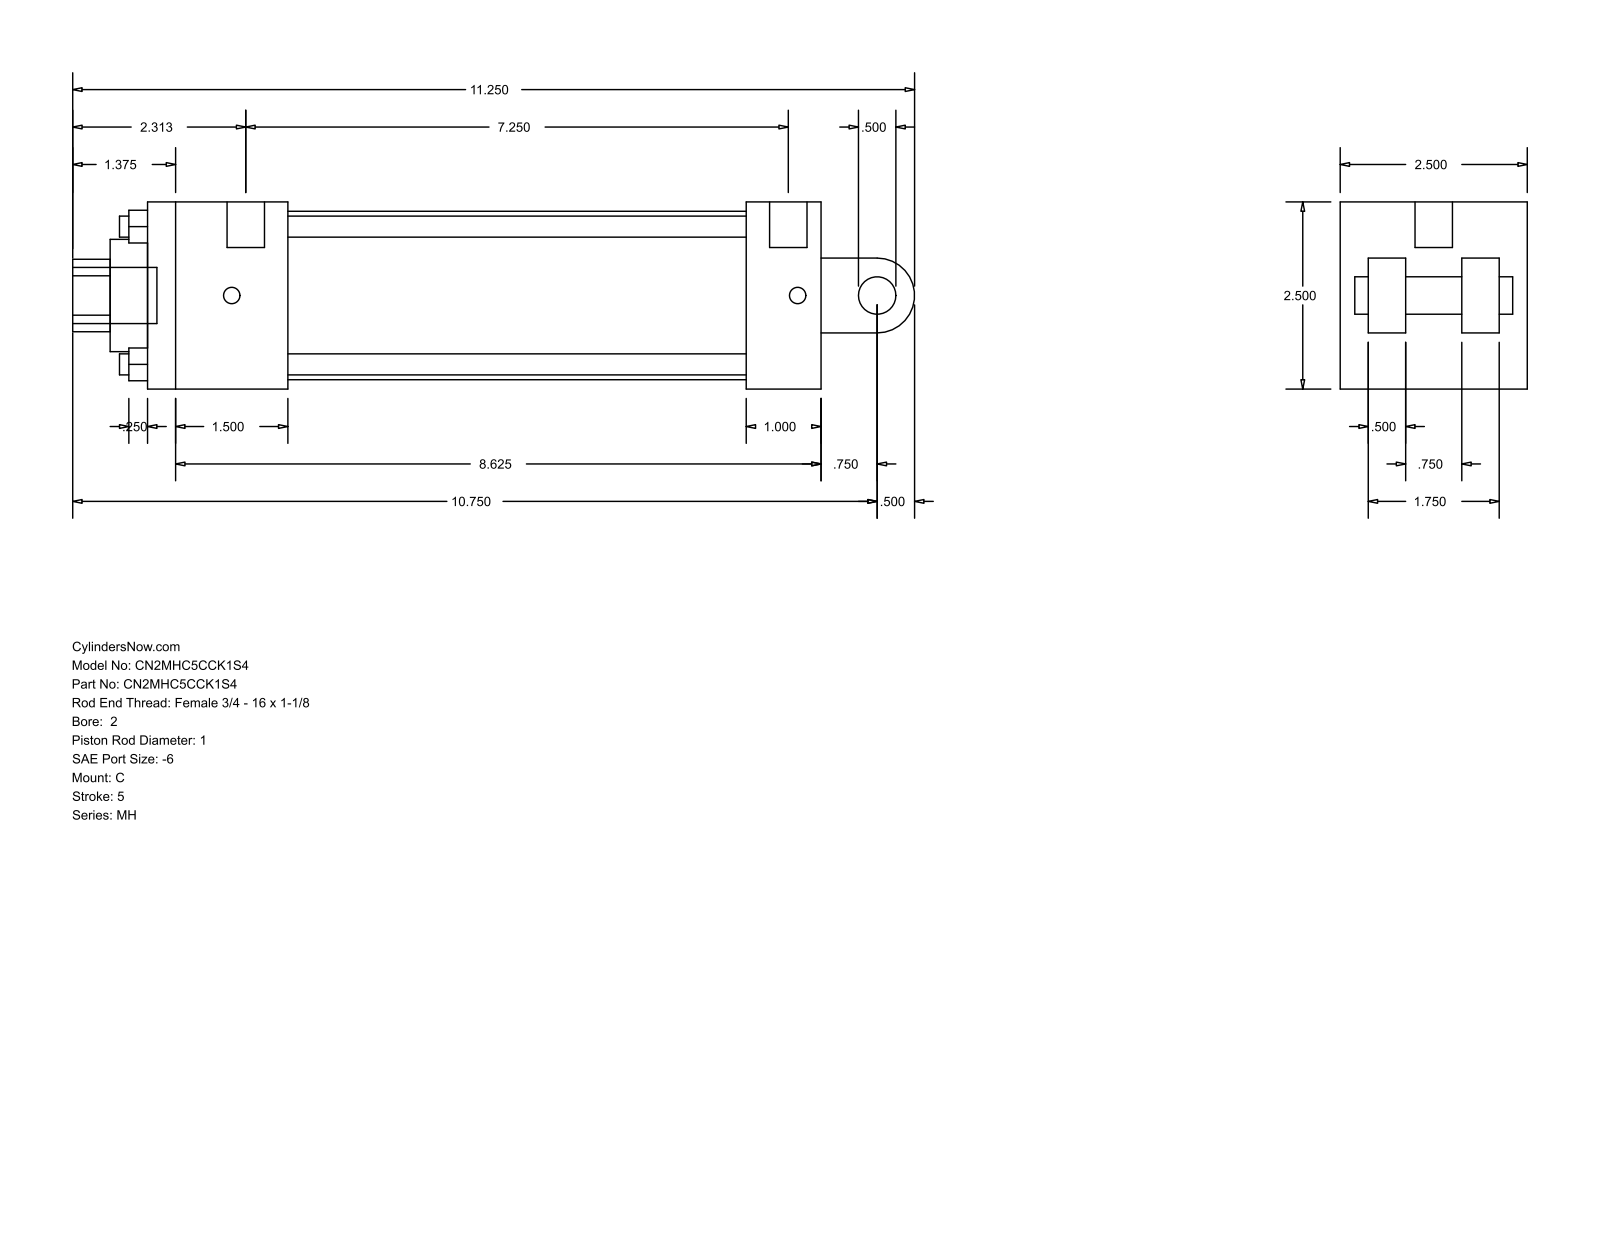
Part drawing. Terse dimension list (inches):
name: MH_C__0200_1
written by: GSSL Pune (CONFIG_CONTROL_DESIGN)
unit: in
bodies: 0 solids, 99 faces (70 planar, 29 cylindrical, 0 other)
size: 11.25 × 2.5 × 2.5
holes: 4× ⌀0.281, 2× ⌀0.219, 1× ⌀0.5, 1× ⌀1, 1× ⌀1.5, 1× ⌀2.25
bosses: 2× ⌀0.5, 2× ⌀0.219, 1× ⌀0.75
rounds: 1× R0.484, 1× R0.5
face distances: 2.5, 9, 0.5, 1, 0.375, 1.875, 2.125, 8, 6.125, 7.125
hole spacings: 1.301, 1.84, 2.602, 0.125
